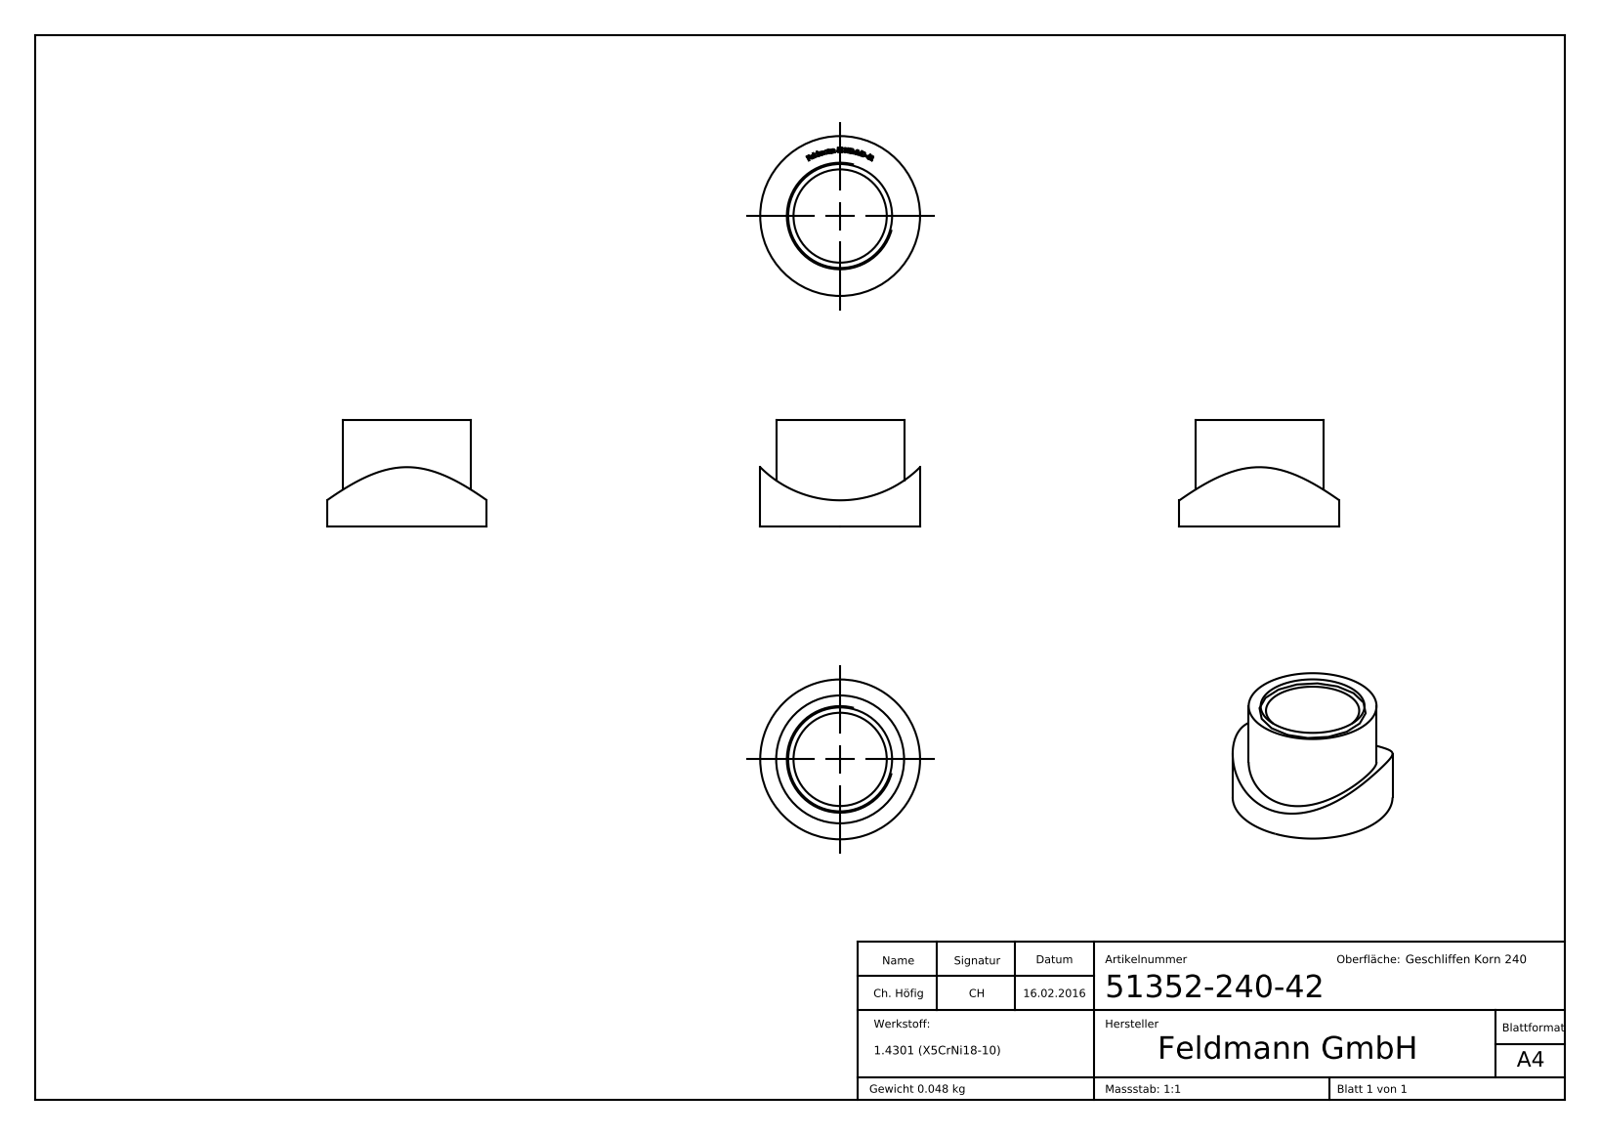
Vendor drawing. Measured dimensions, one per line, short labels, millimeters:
name: 51352-240-42
written by: SolidWorks 2015 (CONFIG_CONTROL_DESIGN)
unit: mm
bodies: 1 solid, 271 faces (155 planar, 7 cylindrical, 109 other)
size: 30 × 30 × 20
volume: 6 034 mm³; area: 3 756 mm²
holes: 1× ⌀17.5
bosses: 1× ⌀30, 1× ⌀24
rounds: 1× R21.2
face distances: 20, 19.9, 0.4, 0.32, 0.43, 0.36, 1.17, 2.53, 0.79, 0.39
